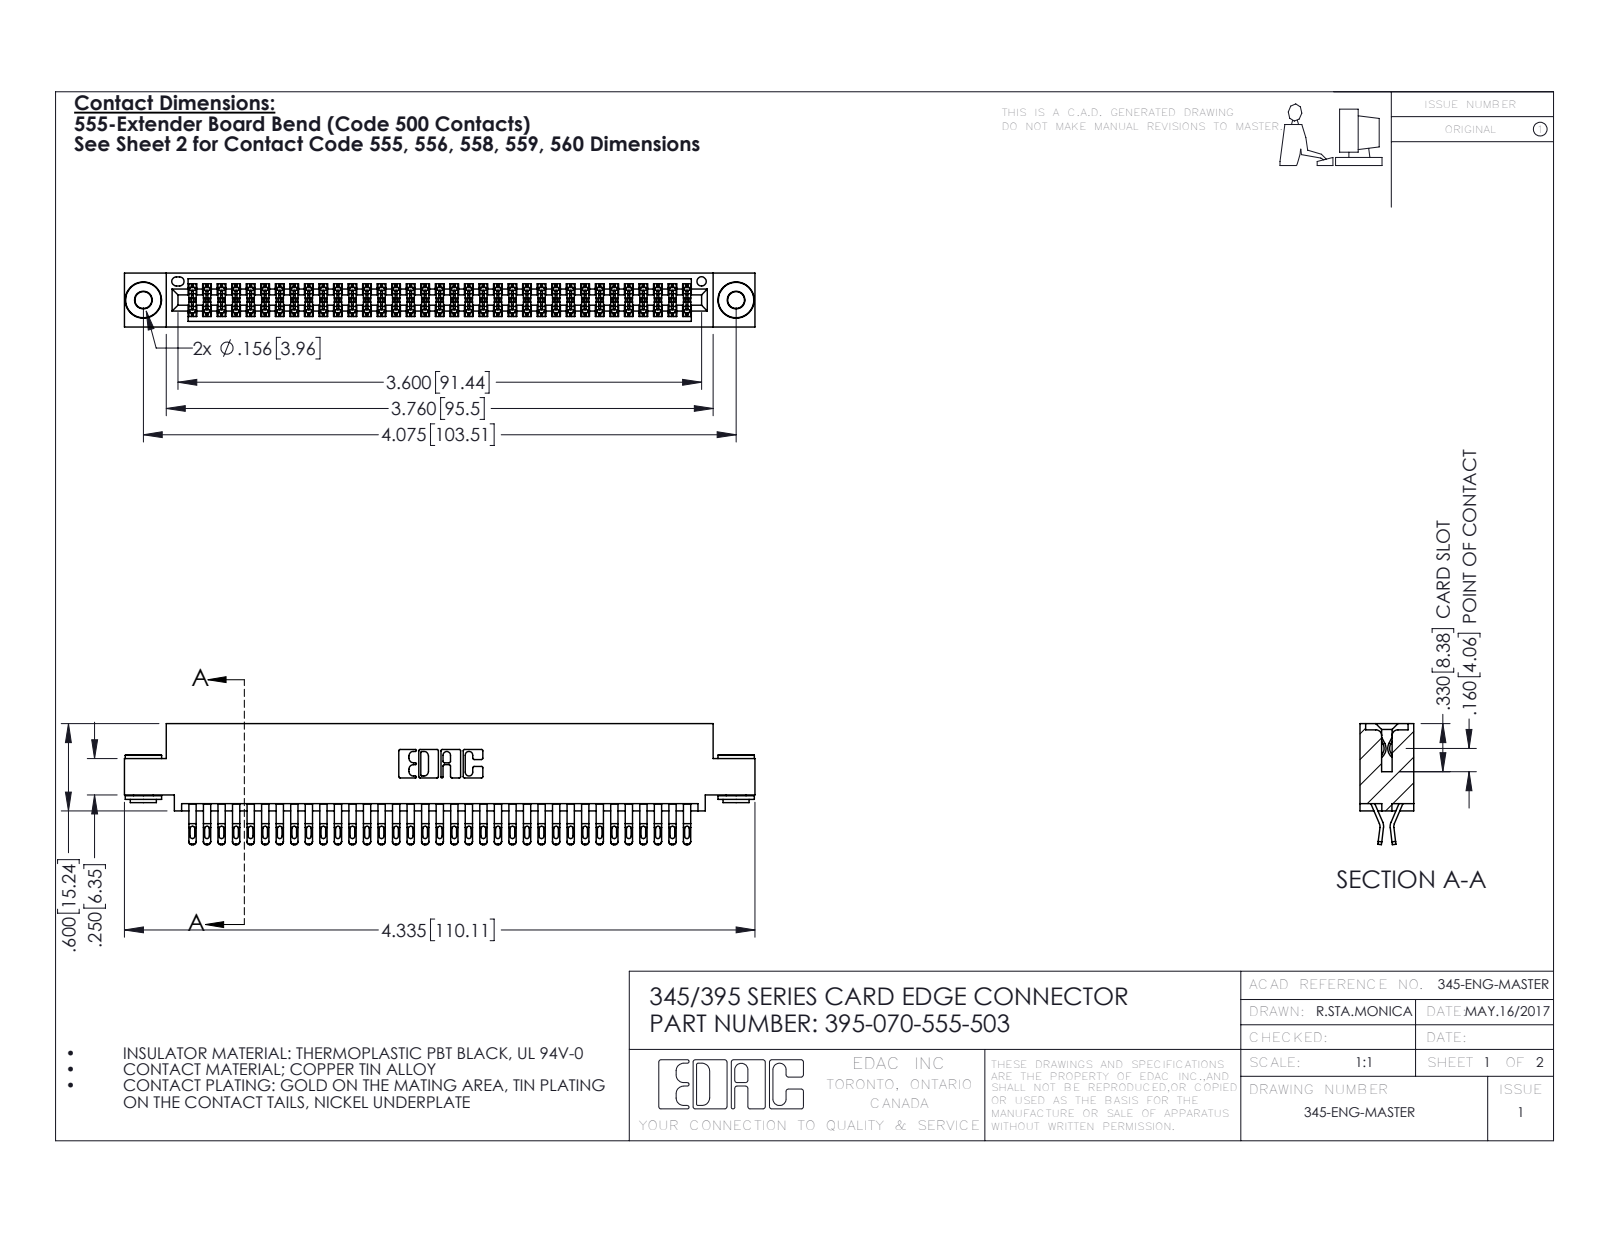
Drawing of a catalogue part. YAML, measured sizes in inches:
part_name: "345-292-001_555 Tail; 345-250-002_345-250-002-102; 395-070-555-503; 345 Part_0.110 Offset - 0.156 Dia-TH"
step_written_by: "SolidWorks 2016 (CONFIG_CONTROL_DESIGN)"
units: inches
bodies: {solids: 73, faces: 4088, planar: 2264, cylindrical: 1816, other: 8}
overall_size: [4.335, 0.832, 0.37]
volume: 0.658
surface_area: 26.05
round_holes:
  - {diameter: 0.116, count: 2}
  - {diameter: 0.156, count: 2}
  - {diameter: 0.064, count: 1}
round_bosses_or_shafts:
  - {diameter: 0.25, count: 2}
  - {diameter: 0.18, count: 2}
  - {diameter: 0.136, count: 2}
partial_cylinders:
  - {radius: 0.016, count: 175}
  - {radius: 0.02, count: 140}
  - {radius: 0.006, count: 105}
  - {radius: 0.01, count: 22}
  - {radius: 0.007, count: 6}
  - {radius: 0.031, count: 6}
  - {radius: 0.026, count: 3}
  - {radius: 0.01, count: 2}
face_to_face_distances: [0.072, 0.298, 0.025, 0.37, 0.2, 0.098, 0.272, 0.225, 0.175, 0.149]
hole_center_spacings: [0.27, 3.839, 4.075]
